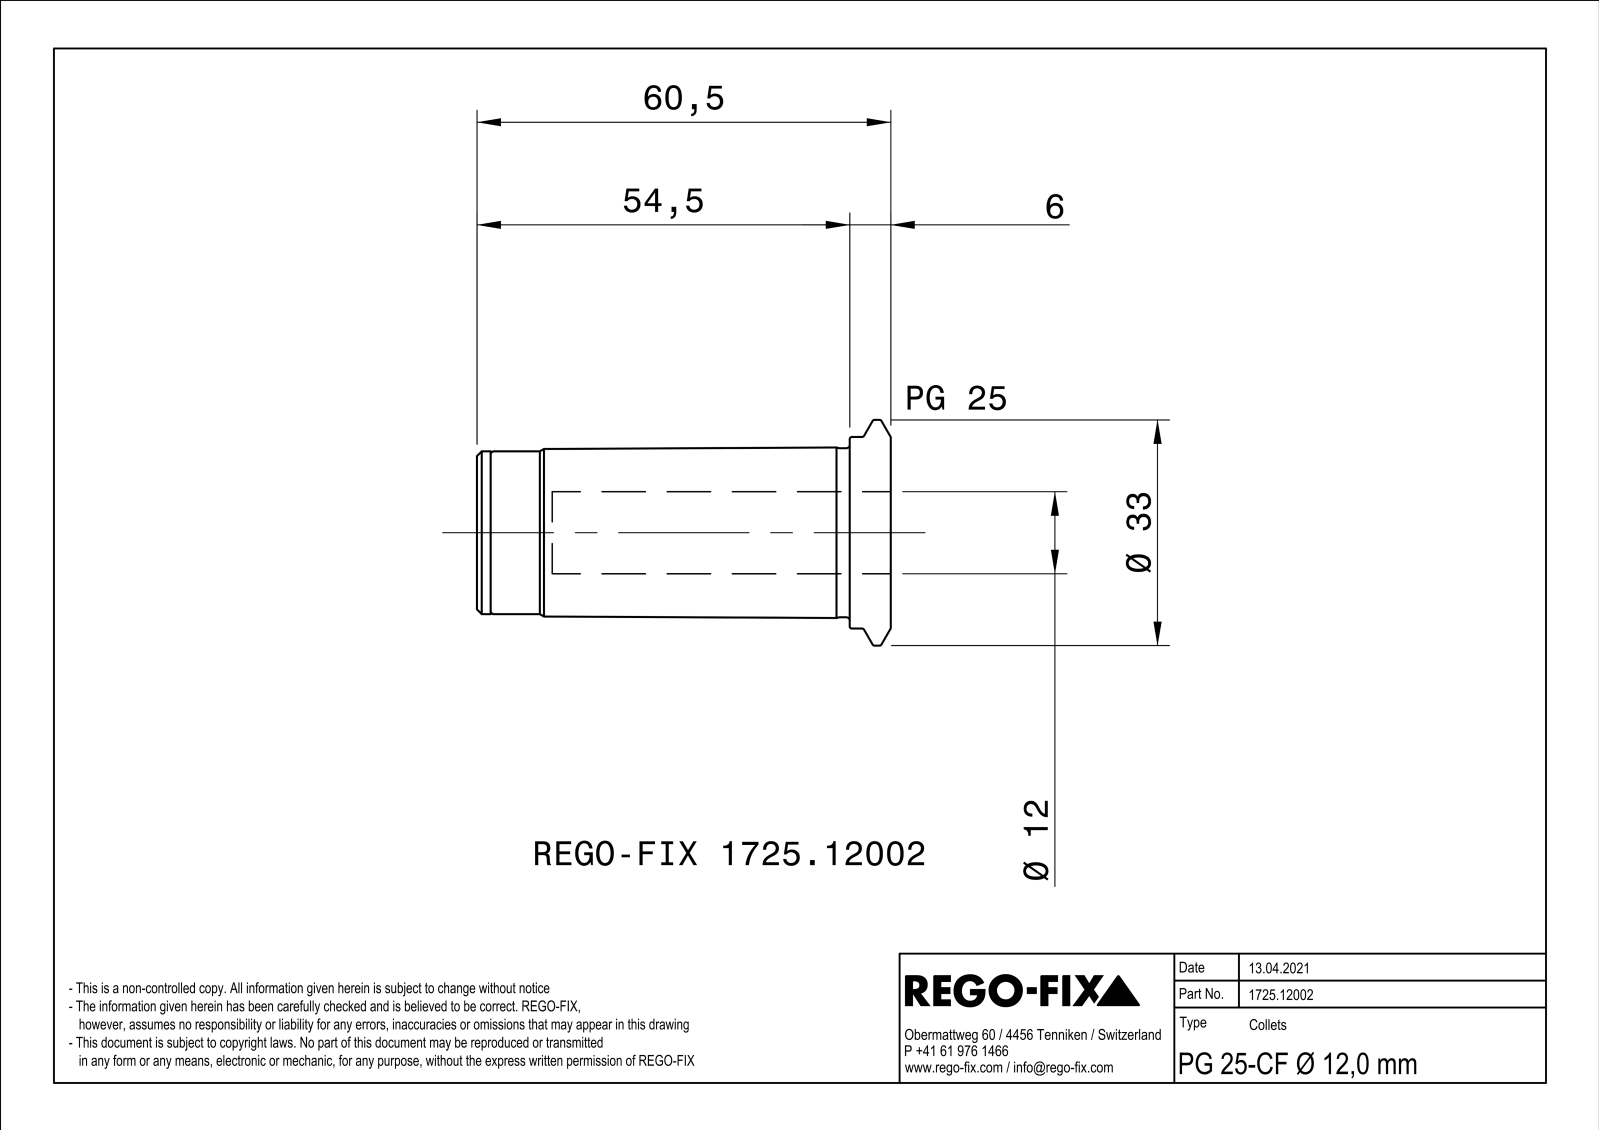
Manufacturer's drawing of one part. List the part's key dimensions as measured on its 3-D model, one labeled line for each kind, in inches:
Part name (STEP PRODUCT): NOCUT
STEP written by: SIEMENS PLM Software Solid Edge ST10 (AUTOMOTIVE_DESIGN)
Units: inches
Bodies: 1 solid, 89 faces (23 planar, 27 cylindrical, 39 other)
Overall size (bounding box): 2.382 × 1.299 × 1.299
Volume: 1.353 in³ · Surface area: 17.34 in²
Round holes (diameter × count): ⌀0.098 ×3, ⌀0.205 ×1, ⌀0.272 ×1, ⌀0.323 ×1, ⌀0.472 ×1, ⌀0.824 ×1, ⌀0.874 ×1
Round bosses / shafts (diameter × count): ⌀1.299 ×1, ⌀1.102 ×1, ⌀0.972 ×1, ⌀0.937 ×1, ⌀0.803 ×1
Partial cylindrical surfaces — rounded edges, fillets, slot ends (radius × count): R0.03 ×3
Main face-to-face distances: 0.039, 2.382, 2.071, 0.311, 2.303, 0.232, 0.079, 1.969, 0.102, 0.335
Hole centre spacings: 0.305, 0.529, 0.528
